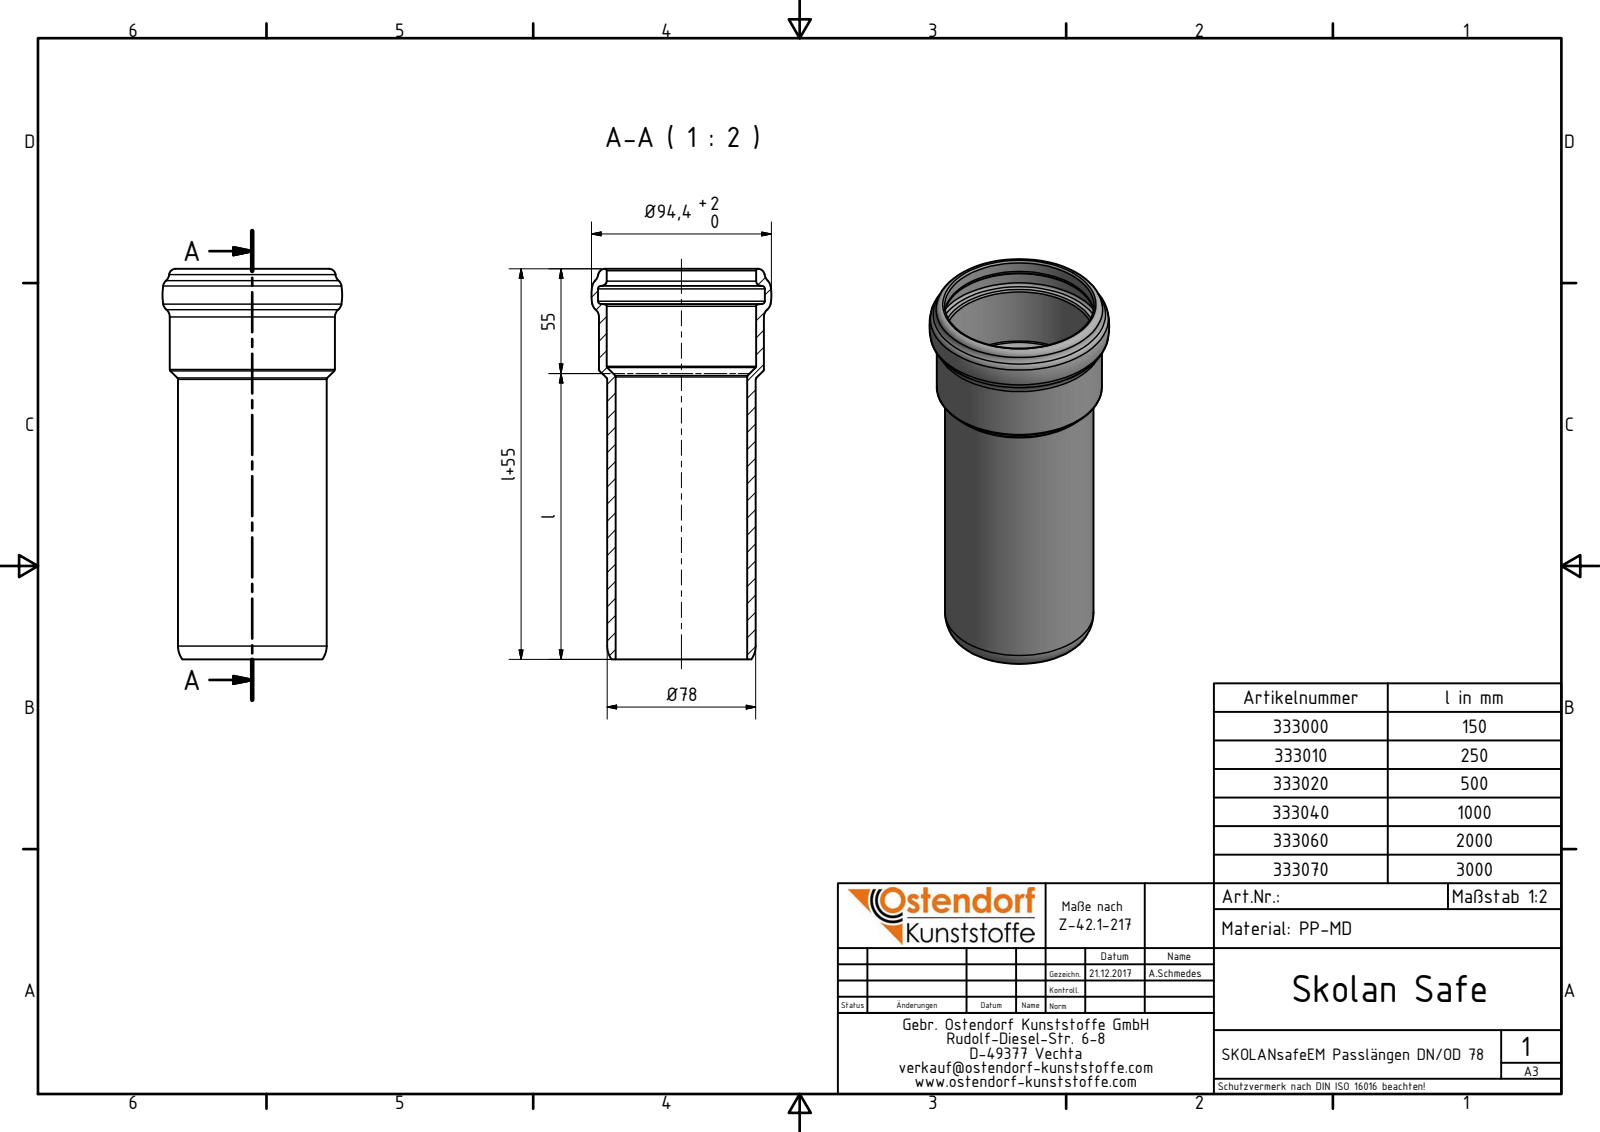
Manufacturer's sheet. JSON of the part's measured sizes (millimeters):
{"part_name": "333040 SKOLANsafeEM Passlängen DN_OD 78x1000", "step_written_by": "Autodesk Inventor 2016 (AUTOMOTIVE_DESIGN)", "units": "millimeters", "bodies": {"solids": 1, "faces": 27, "planar": 1, "cylindrical": 6, "other": 20}, "overall_size": [1055, 94.4, 94.4], "volume_mm3": 1102000, "surface_area_mm2": 495237, "round_holes": [[69, 1], [78.5, 1], [87.6, 1]], "round_bosses_or_shafts": [[86.7, 1], [78, 1]]}
